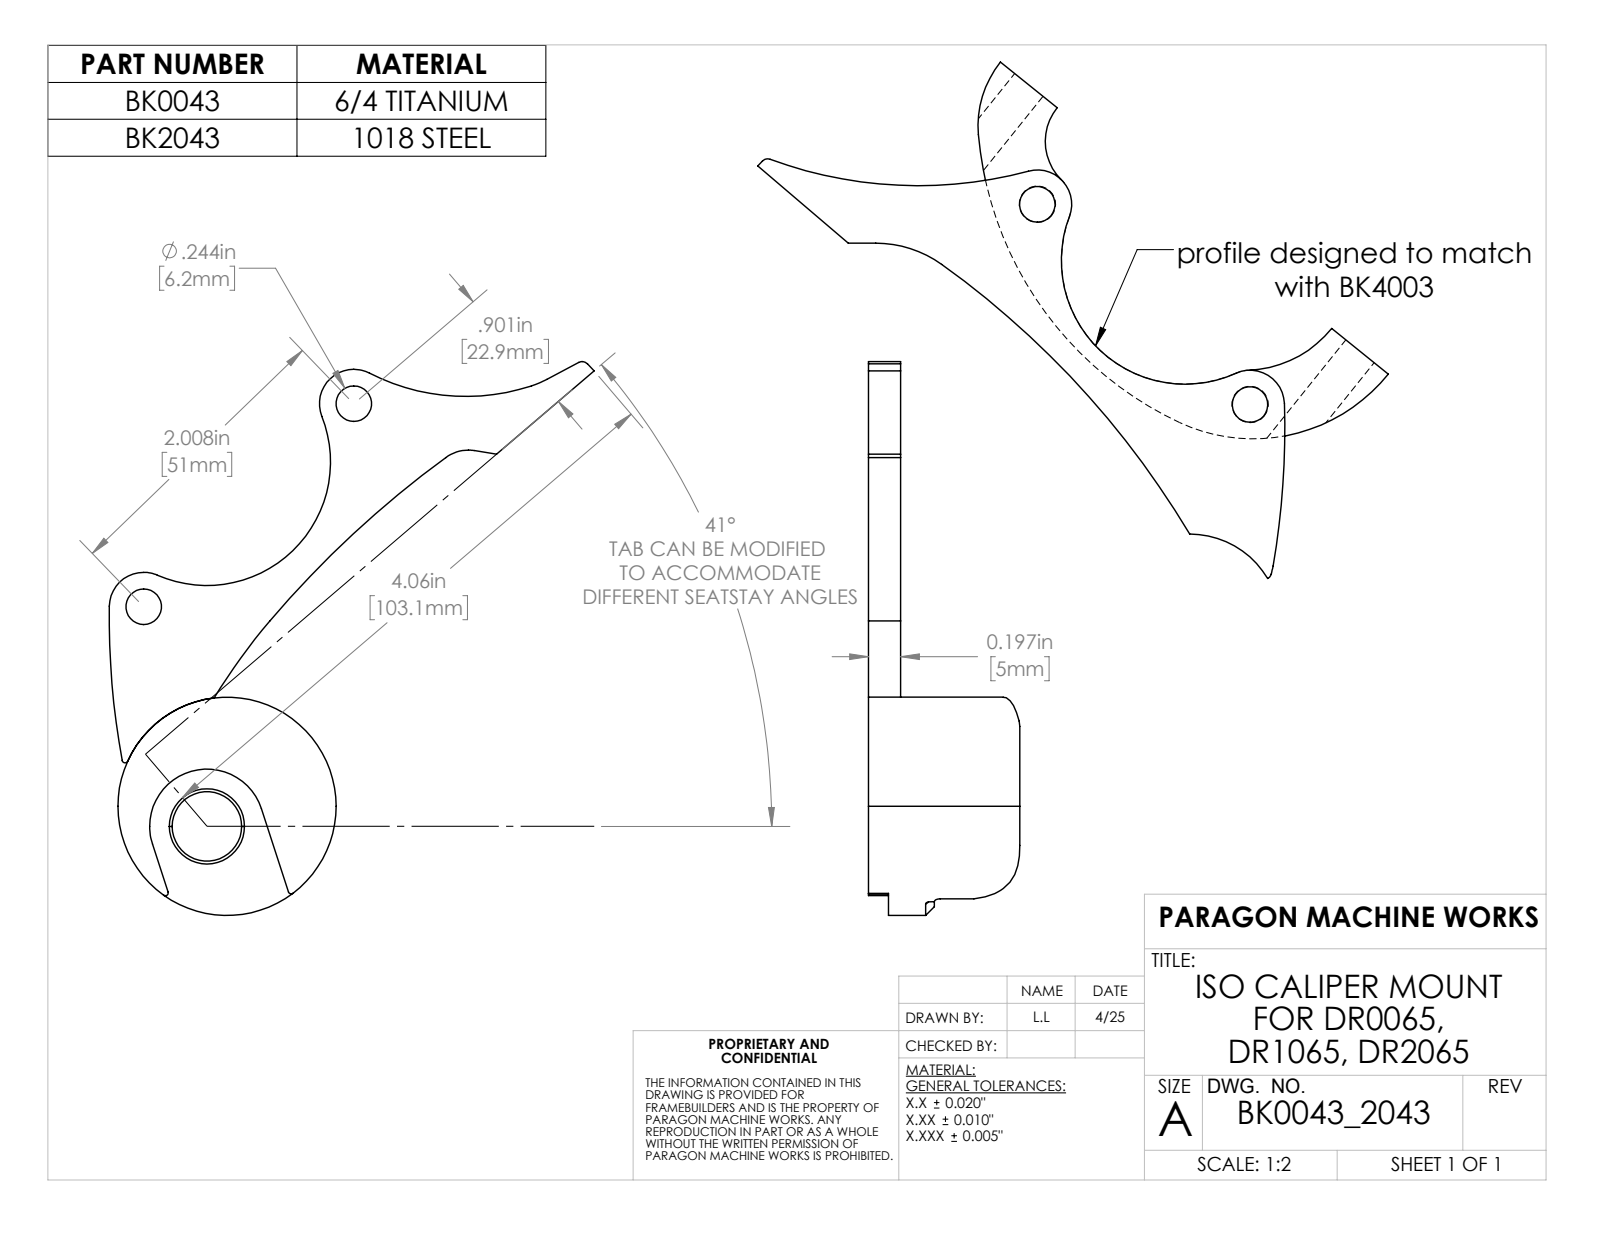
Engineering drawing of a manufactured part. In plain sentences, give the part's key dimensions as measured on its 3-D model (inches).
The part is named "BK0043". Its 3-D file was written by "SolidWorks 2018 (AUTOMOTIVE_DESIGN)". It is 1 solid with 25 faces: 6 planar, 19 cylindrical and 0 other. Overall it measures 3.333 by 2.808 by 0.22 inches. Its volume is 0.423 cubic inches and its surface area 6.432 square inches. Round holes: 2 of diameter 0.244. Partial cylindrical surfaces (rounded edges, fillets, slot ends): 2 of radius 0.236, 1 of radius 0.05, 1 of radius 0.264, 1 of radius 0.69, 1 of radius 0.75, 1 of radius 0.85, 1 of radius 1.446, 1 of radius 4.105. The main face-to-face distances are 0.22. The hole center spacings are 2.008.
